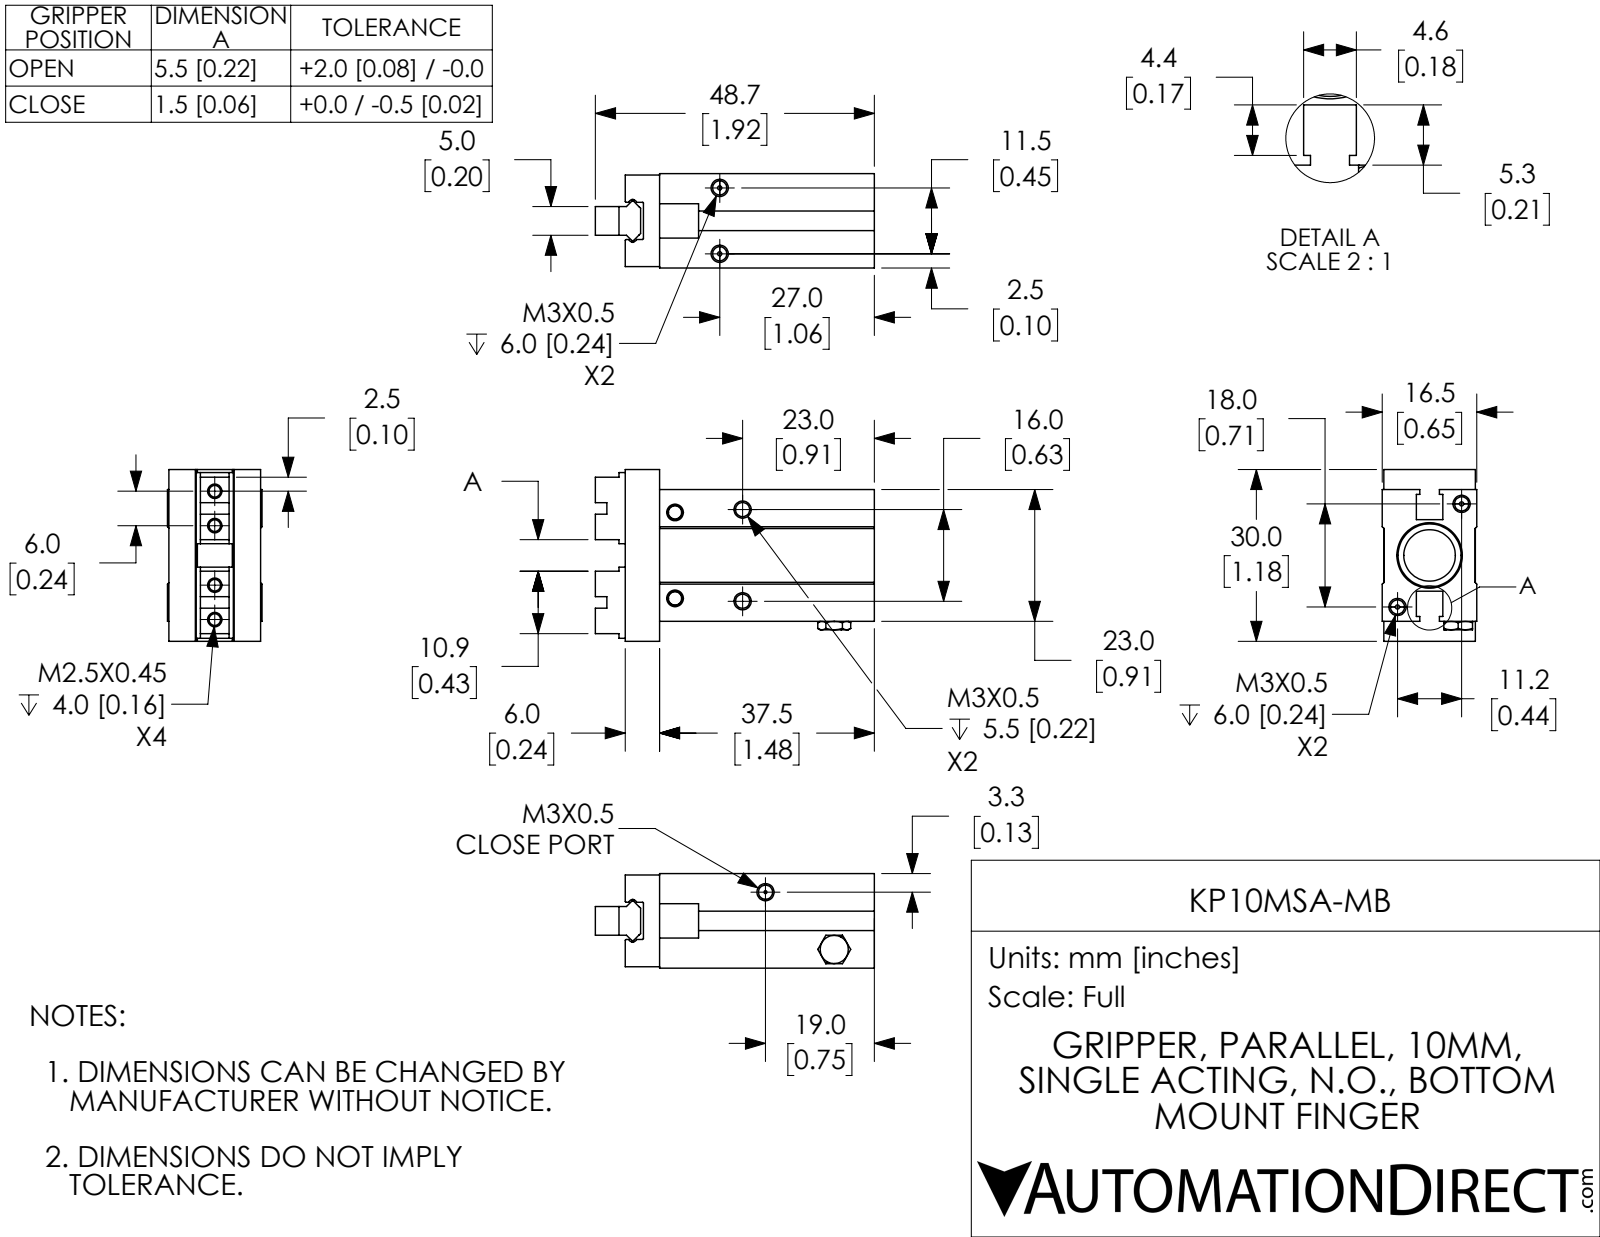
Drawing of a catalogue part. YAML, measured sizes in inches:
part_name: "KP10MSA-MB-1; KP10MSA-MB; KP10MSA-MB-3; KP10MSA-MB-2"
step_written_by: "SolidWorks 2017 (CONFIG_CONTROL_DESIGN)"
units: inches
bodies: {solids: 3, faces: 240, planar: 126, cylindrical: 56, other: 58}
overall_size: [1.917, 1.181, 0.65]
volume: 0.871
surface_area: 11.45
round_holes:
  - {diameter: 0.079, count: 4}
  - {diameter: 0.097, count: 4}
  - {diameter: 0.097, count: 4}
  - {diameter: 0.02, count: 2}
  - {diameter: 0.119, count: 2}
  - {diameter: 0.354, count: 1}
  - {diameter: 0.433, count: 1}
partial_cylinders:
  - {radius: 0.008, count: 4}
  - {radius: 0.01, count: 2}
  - {radius: 0.03, count: 2}
face_to_face_distances: [0.638, 0.207, 0.197, 0.404, 0.222, 0.234, 0.415, 0.65, 0.217, 0.906]
hole_center_spacings: [0.205, 0.236, 0.237, 0.267, 0.417, 0.441, 0.601, 0.646]
